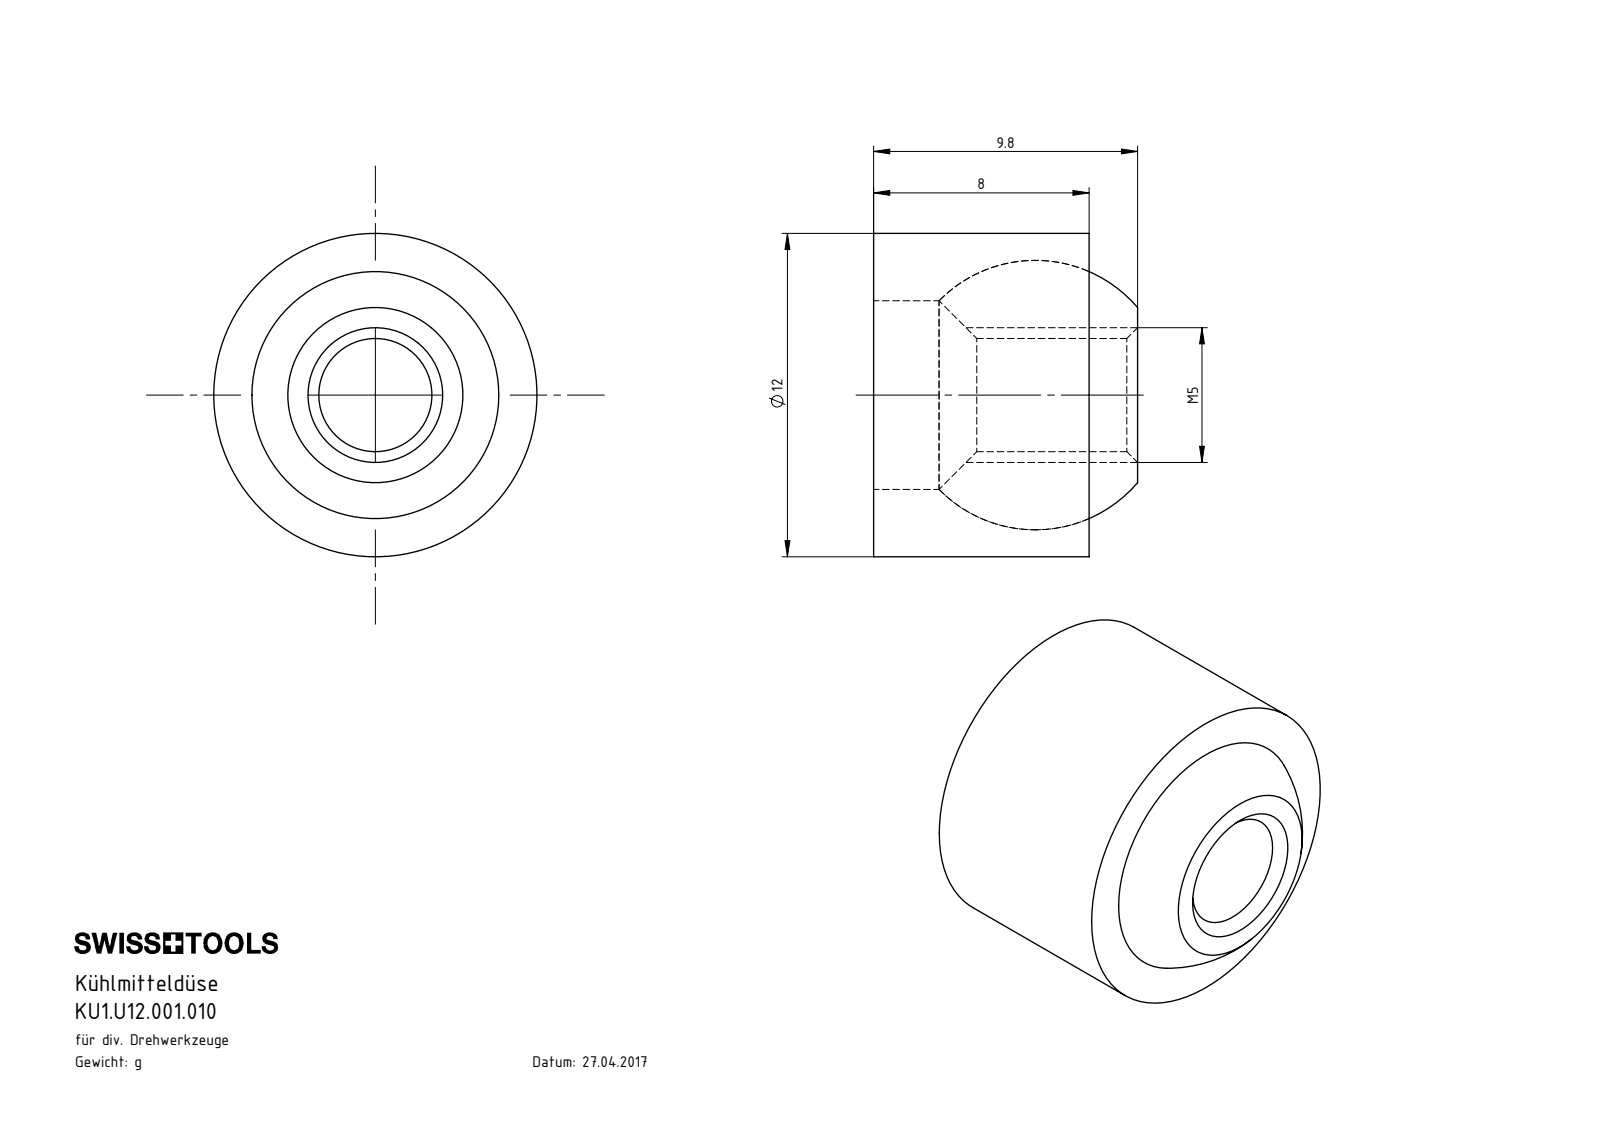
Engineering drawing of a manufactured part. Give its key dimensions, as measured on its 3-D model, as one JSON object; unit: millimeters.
{"part_name": "KU1-U12.001.010_2; KU1-U12.001.010_1; KU1.U12.001.010", "step_written_by": "SolidWorks 2017 (AUTOMOTIVE_DESIGN)", "units": "millimeters", "bodies": {"solids": 2, "faces": 17, "planar": 3, "cylindrical": 6, "other": 8}, "overall_size": [12, 12, 9.8], "volume_mm3": 785, "surface_area_mm2": 1013, "round_holes": [[4.2, 1], [7, 1]], "round_bosses_or_shafts": [[12, 1]], "face_to_face_distances": [8, 9.8, 1.8]}
